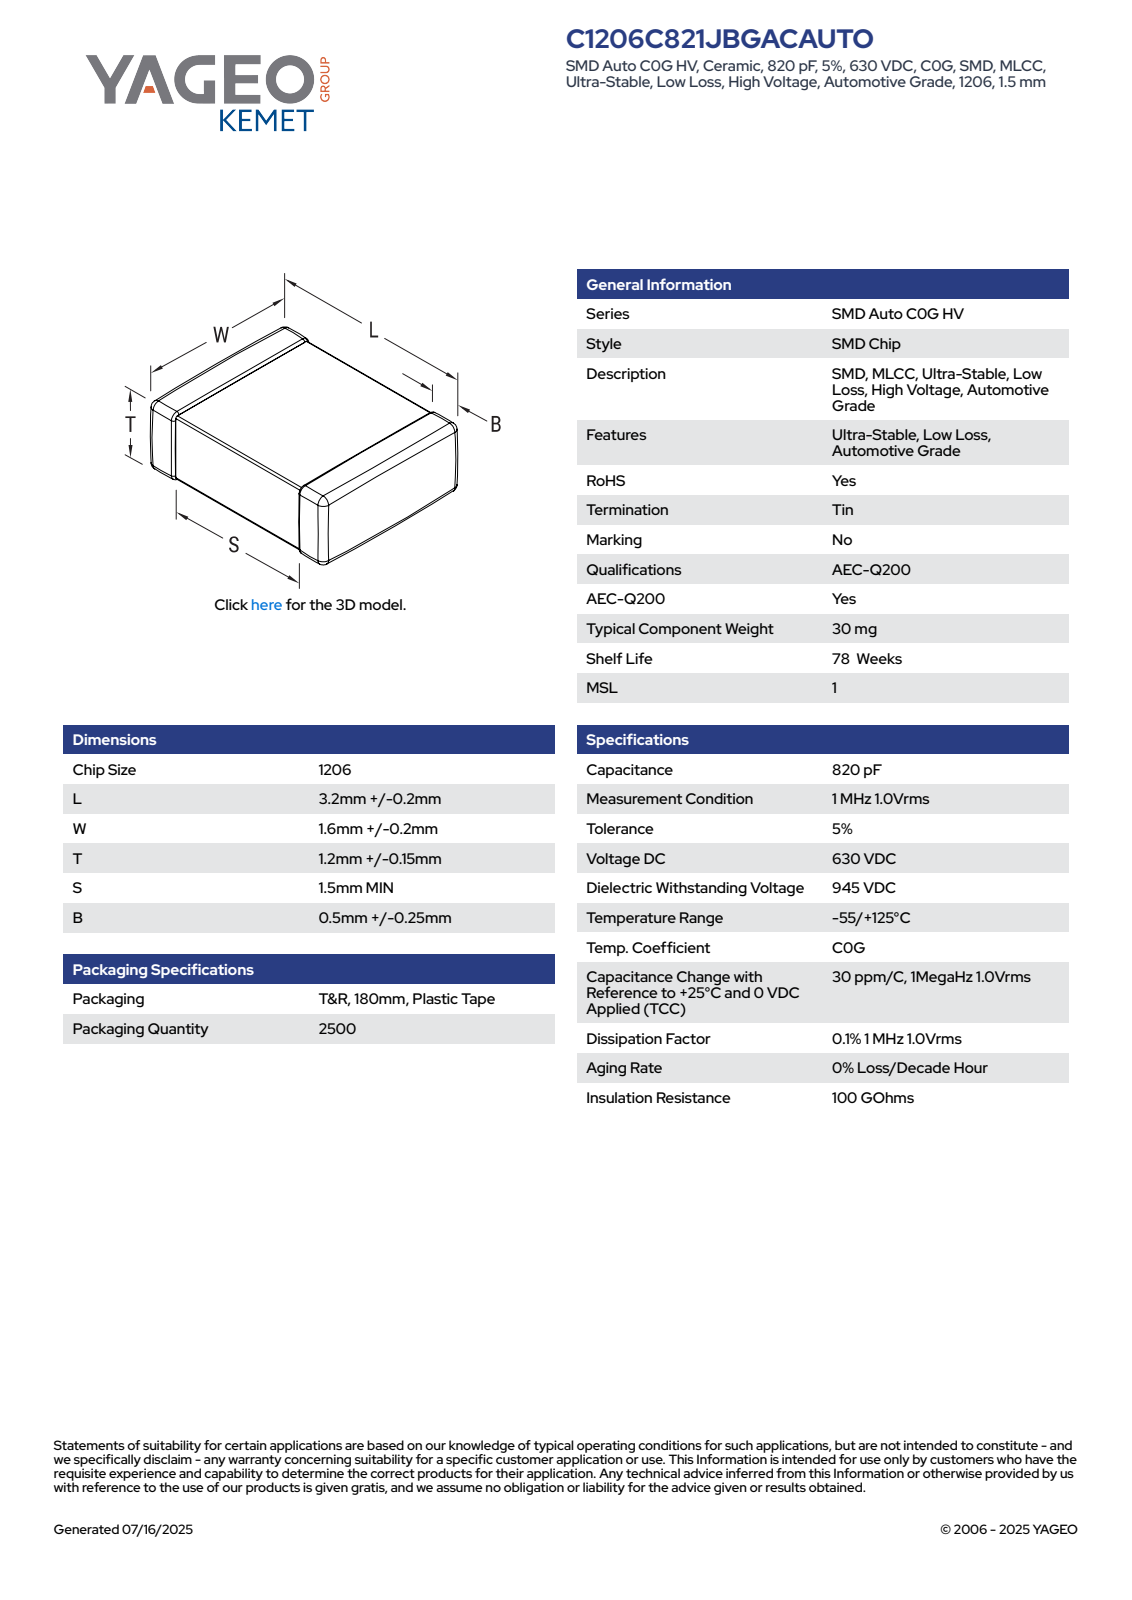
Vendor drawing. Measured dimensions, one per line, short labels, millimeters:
name: CCS_CCSTDNOS_1206_L3.4W1.8T1.35B0.75
written by: SolidWorks 2014 (AUTOMOTIVE_DESIGN)
unit: mm
bodies: 4 solids, 125 faces (71 planar, 38 cylindrical, 16 other)
size: 3.4 × 1.8 × 1.35
volume: 8 mm³; area: 26 mm²
face distances: 1.31, 1.76, 1.27, 1.35, 1.72, 3.4, 1.8, 1.32, 1.28, 0.99
